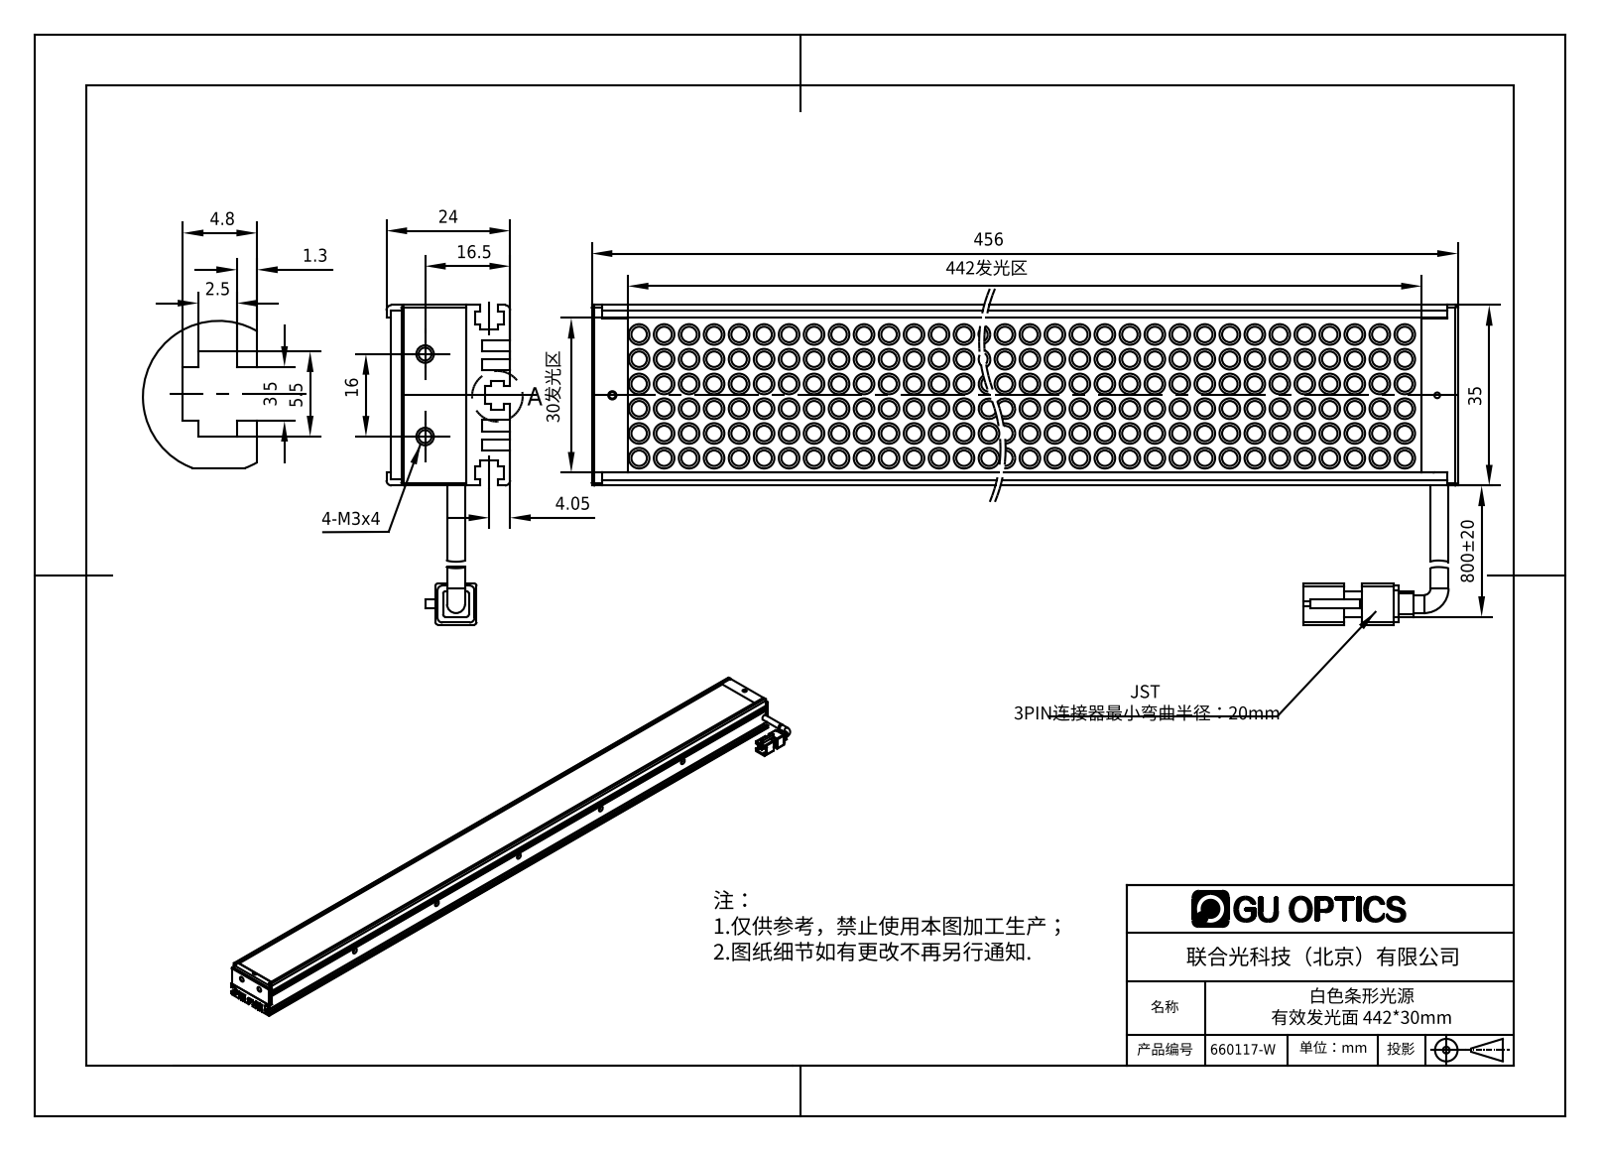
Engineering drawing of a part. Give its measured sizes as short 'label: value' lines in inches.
name: 660117-W
written by: SolidWorks 2016 (AUTOMOTIVE_DESIGN)
unit: in
bodies: 8 solids, 3753 faces (813 planar, 2279 cylindrical, 661 other)
size: 17.953 × 2.441 × 0.945
volume: 12.13 in³; area: 355.3 in²
holes: 5× ⌀0.063, 5× ⌀0.067, 2× ⌀0.059, 2× ⌀0.098, 2× ⌀0.11, 2× ⌀0.118, 1× ⌀0.043, 1× ⌀0.049, 1× ⌀0.079
bosses: 546× ⌀0.157, 546× ⌀0.118, 2× ⌀0.138
rounds: 12× R0.039, 8× R0.02, 1× R0.065
face distances: 0.079, 0.087, 0.339, 0.039, 0.098, 0.157, 0.354, 0.417, 0.425, 0.496
hole spacings: 2.953, 5.906, 17.638, 0.276, 2.914, 2.921, 5.867, 5.87
